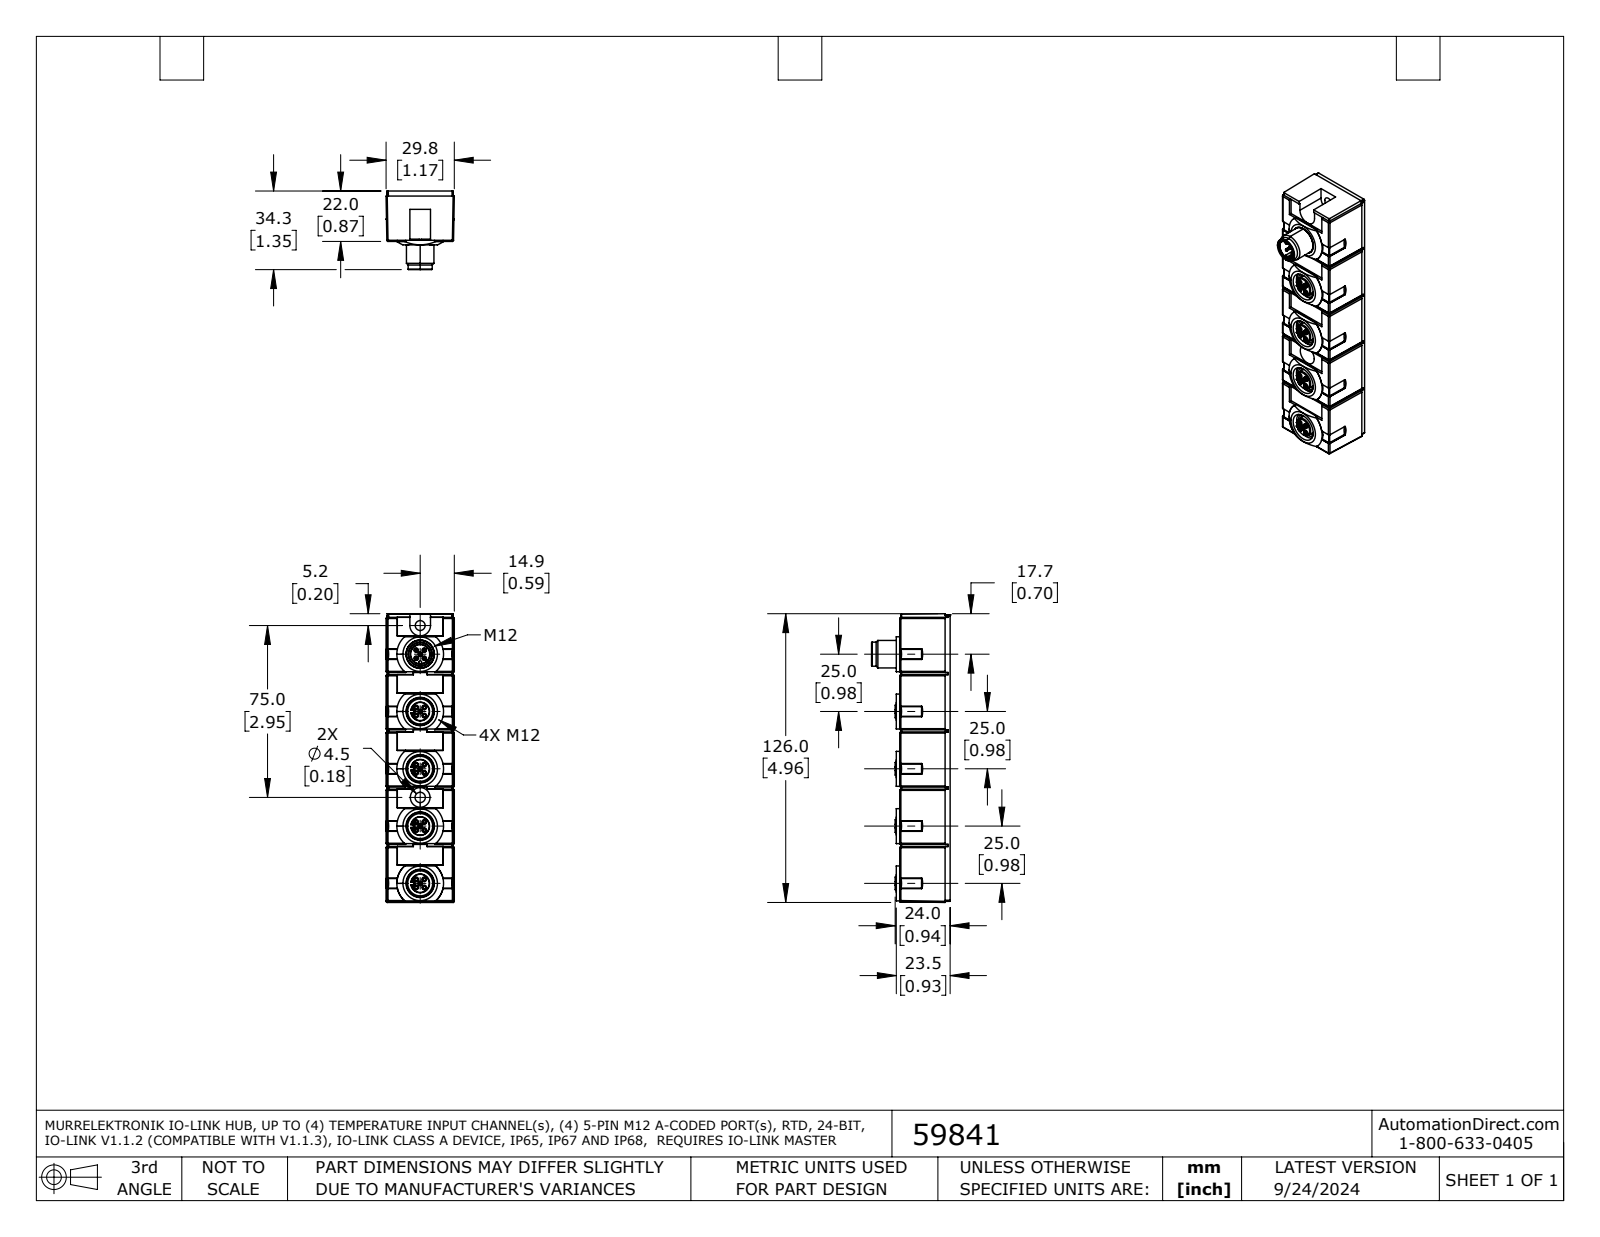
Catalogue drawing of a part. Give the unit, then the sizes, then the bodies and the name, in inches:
Units: inches
Overall size (bounding box): 4.961 × 1.35 × 1.173
Round holes (diameter × count): ⌀0.047 ×20, ⌀0.049 ×5, ⌀0.075 ×5, ⌀0.486 ×5, ⌀0.43 ×3, ⌀0.169 ×1, ⌀0.177 ×1, ⌀0.327 ×1, ⌀0.339 ×1, ⌀0.43 ×1
Round bosses / shafts (diameter × count): ⌀0.079 ×20, ⌀0.039 ×5, ⌀0.323 ×4, ⌀0.484 ×1, ⌀0.472 ×1, ⌀0.413 ×1
Partial cylindrical surfaces — rounded edges, fillets, slot ends (radius × count): R0.02 ×36, R0.01 ×30, R0.394 ×20, R0.402 ×5, R0.024 ×4, R0.045 ×4, R0.012 ×2, R0.177 ×2
Main face-to-face distances: 0.866, 0.02, 0.039, 0.827, 0.098, 0.059, 0.079, 1.154, 0.925, 0.846
Hole centre spacings: 0.098, 0.139, 0.984, 0.917, 0.994, 1.056, 1.969, 1.9
Volume: 4.865 in³ · Surface area: 27.56 in²
Bodies: 2 solids, 795 faces (264 planar, 345 cylindrical, 186 other)
Part name (STEP PRODUCT): 59841
STEP written by: SolidWorks 2021 (AUTOMOTIVE_DESIGN)
